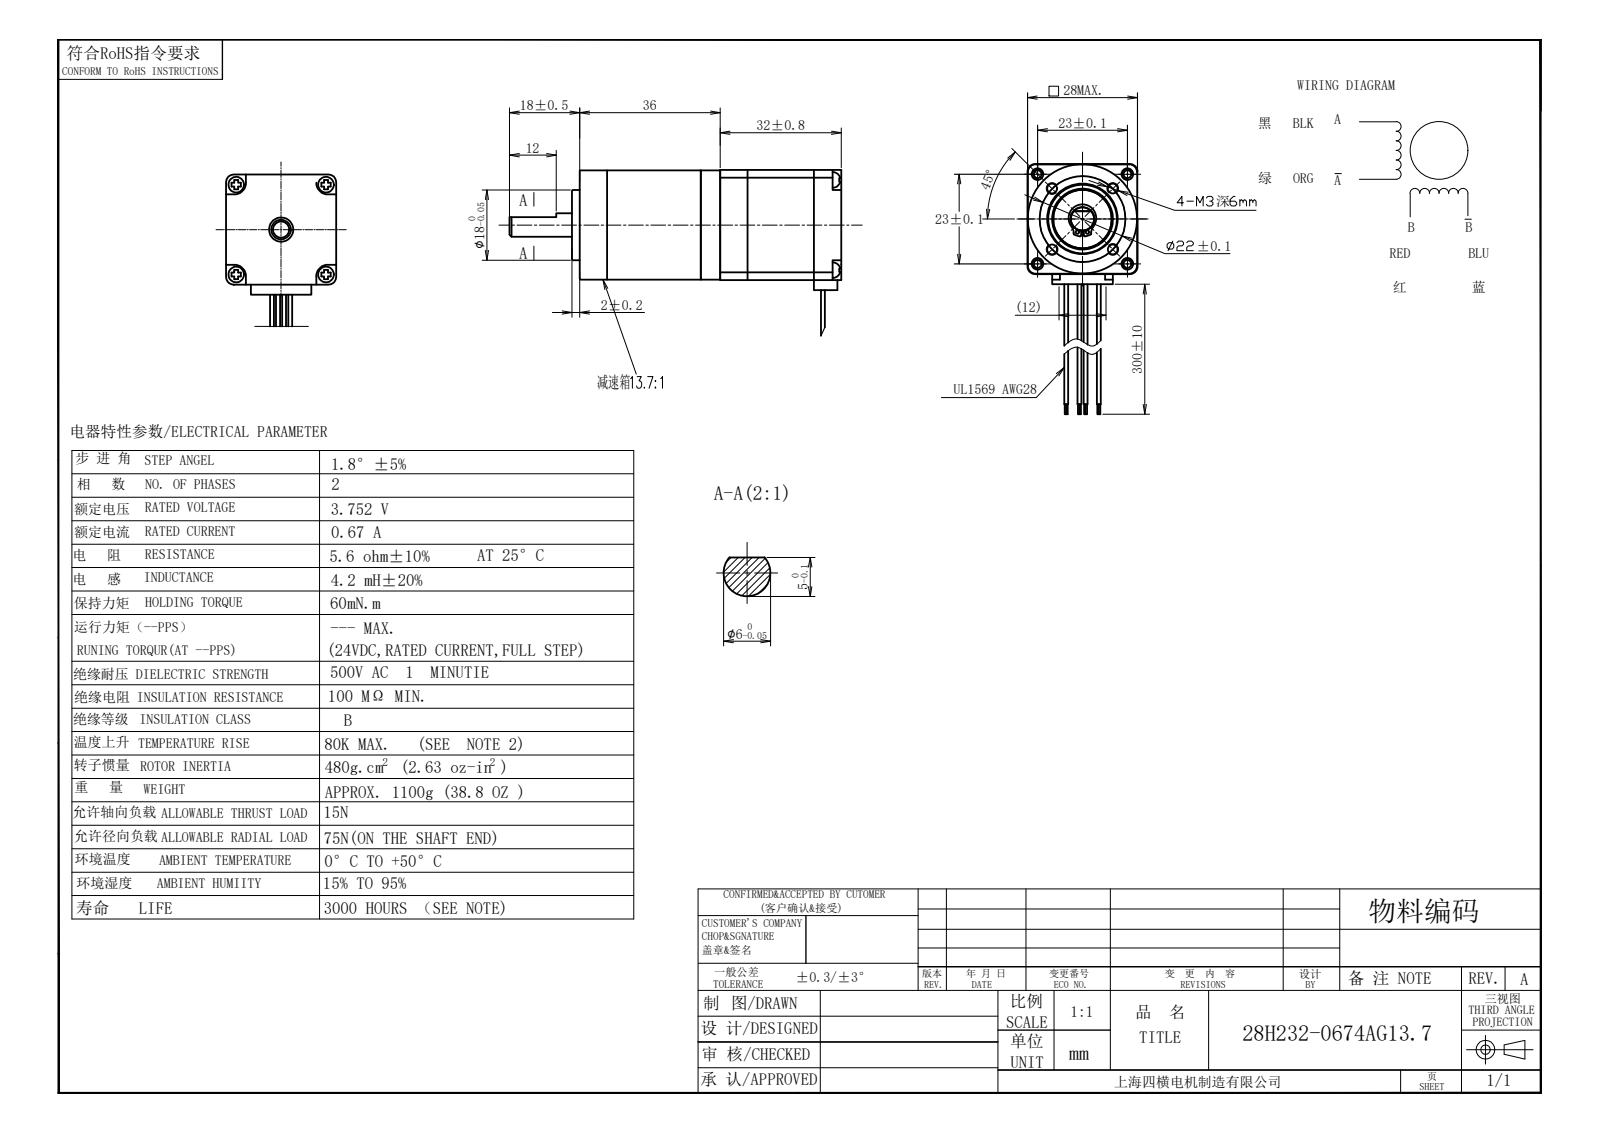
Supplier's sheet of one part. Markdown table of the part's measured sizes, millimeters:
| quantity | value |
| --- | --- |
| part name | 28H232-0674AG13.7; 28定子模型; PLA28-002输出轴; PLA28-003前端盖 (+8 more) |
| STEP written by | SolidWorks 2020 (CONFIG_CONTROL_DESIGN) |
| units | millimeters |
| bodies | 20 solids, 863 faces (174 planar, 575 cylindrical, 114 other) |
| overall size | 82.2 × 55 × 28 |
| volume | 36 442 mm³ |
| surface area | 26 843 mm² |
| round holes (diameter × count) | 2.05 × 8, 3 × 7, 2.9 × 6, 2.5 × 4, 1.2 × 2, 6 × 1, 6.5 × 1, 7.4 × 1, 7.5 × 1, 12 × 1, 12.5 × 1, 13 × 1 |
| round bosses / shafts (diameter × count) | 4.1 × 4, 2.5 × 4, 1.18 × 3, 28 × 1, 22 × 1, 21.5 × 1, 18 × 1, 17.1 × 1 |
| partial cylindrical surfaces (radius × count) | 0.2 × 92, 2.8 × 92, 0.5 × 22, 0.3 × 6, 1 × 4, 2 × 4, 3 × 2, 4.75 × 1 |
| main face-to-face distances | 28, 7, 21, 23.5, 14, 30, 9, 1, 2, 3.5 |
| hole center spacings | 19.64, 23, 5.26, 11, 15.56, 16.26, 27.27, 7.85 |
